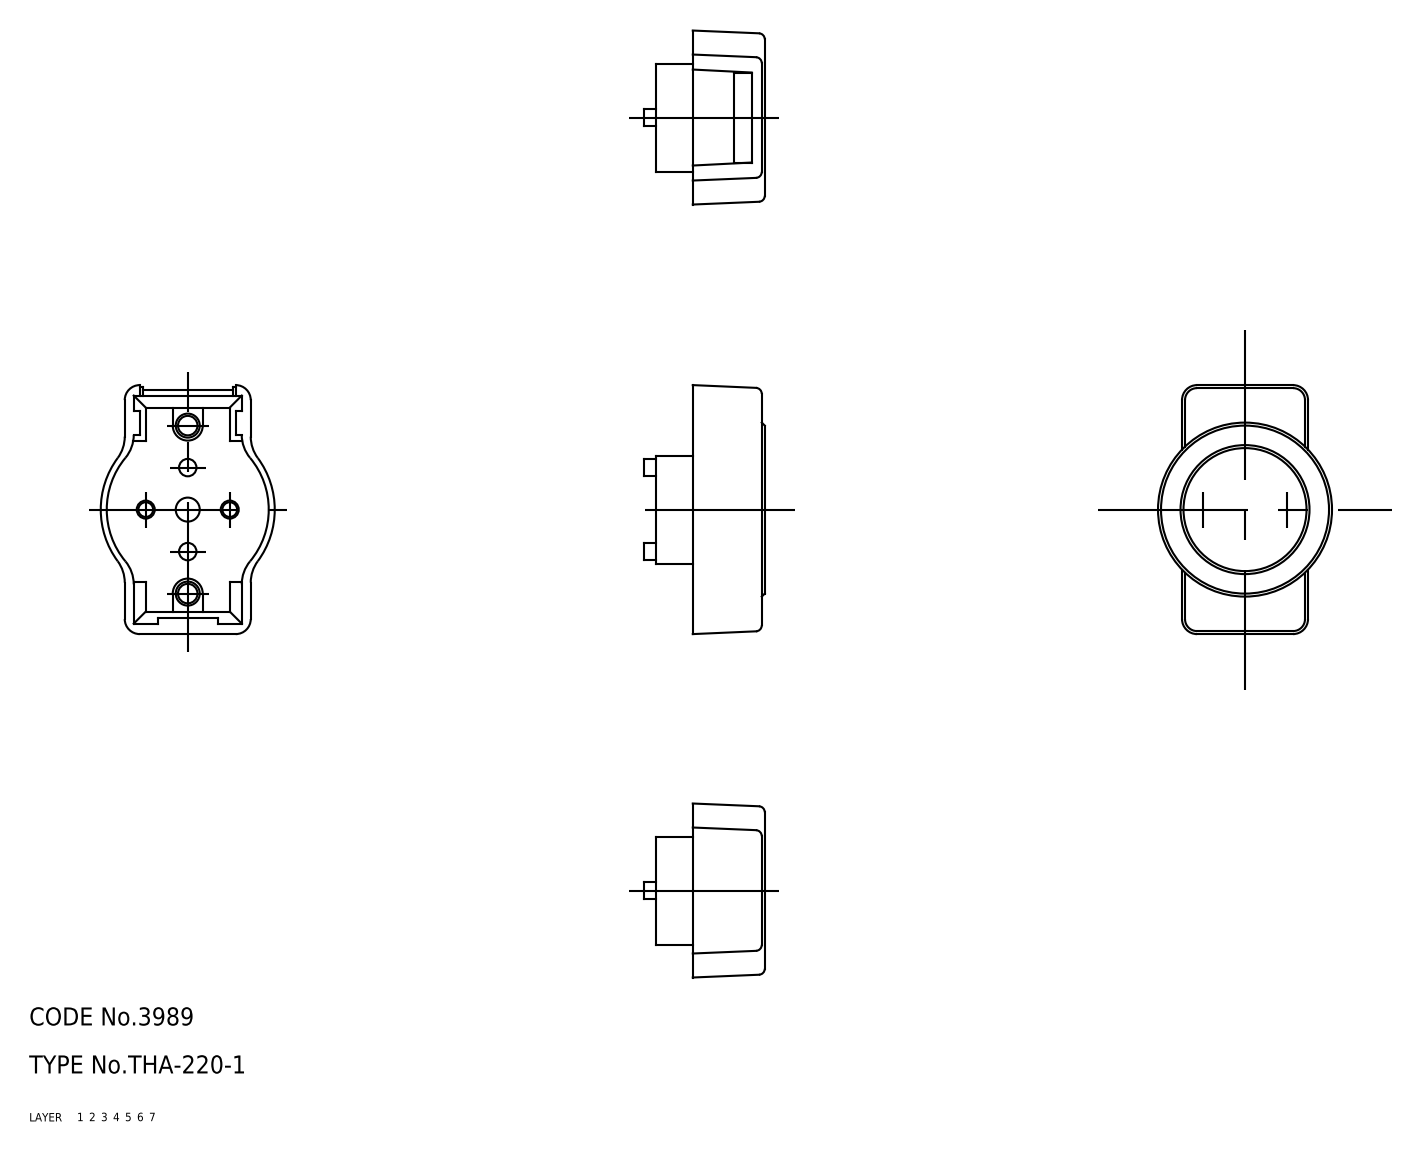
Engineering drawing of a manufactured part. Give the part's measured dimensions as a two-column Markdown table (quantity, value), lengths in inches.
| quantity | value |
| --- | --- |
| part name | cover; base_B; base_A; THA_220_1_24093_36 |
| STEP written by | CADfix (AUTOMOTIVE_DESIGN) |
| units | inches |
| bodies | 3 solids, 130 faces (0 planar, 0 cylindrical, 130 other) |
| overall size | 1.634 × 1.142 × 0.795 |
| volume | 0.529 in³ |
| surface area | 14.28 in² |
